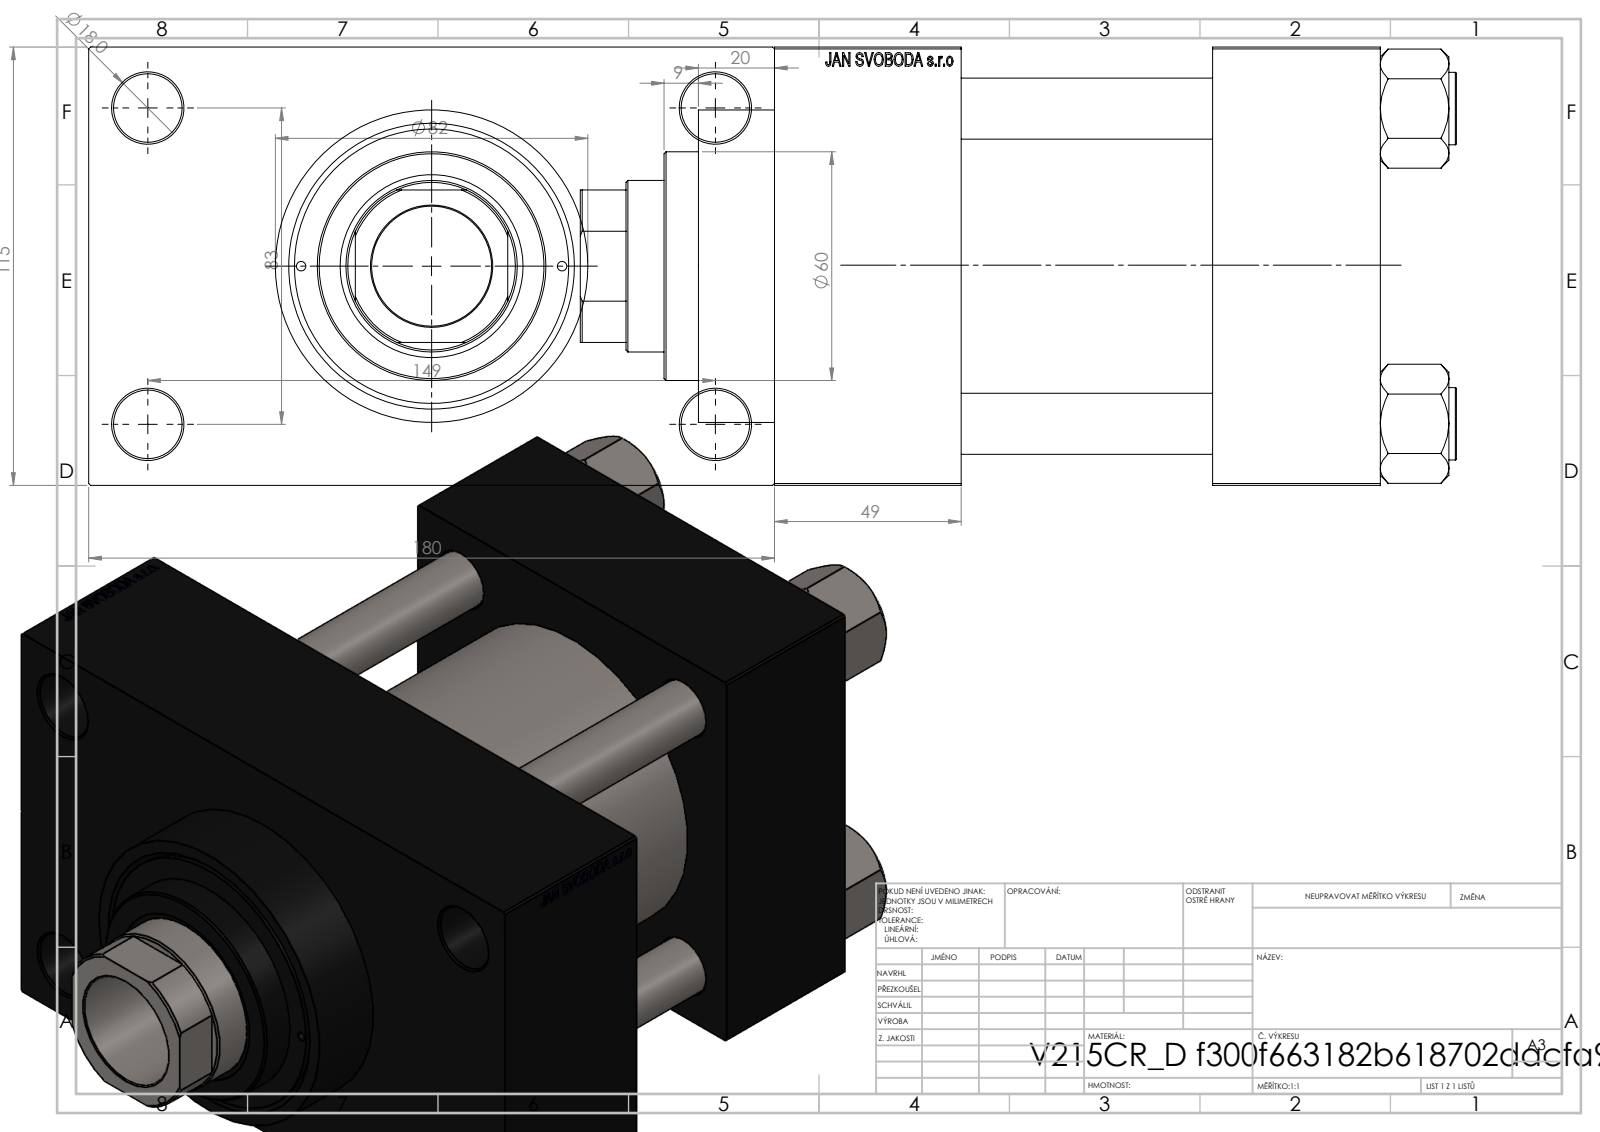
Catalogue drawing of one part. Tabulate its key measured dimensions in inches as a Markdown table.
| quantity | value |
| --- | --- |
| part name | V215CR_D_Body; V215CR_VCP_D; V215CR_D_TYCINKA; NUT_M5_D (+1 more) |
| STEP written by | SolidWorks 2019 (CONFIG_CONTROL_DESIGN) |
| units | inches |
| bodies | 11 solids, 1159 faces (547 planar, 92 cylindrical, 520 other) |
| overall size | 9.055 × 7.087 × 4.528 |
| volume | 122.3 in³ |
| surface area | 468.6 in² |
| round holes (diameter × count) | 0.63 × 4, 0.709 × 4, 0.098 × 2, 0.276 × 2, 1.041 × 2, 1.378 × 2, 1.24 × 1, 1.772 × 1, 1.89 × 1, 2.402 × 1, 2.835 × 1, 3.15 × 1 |
| round bosses / shafts (diameter × count) | 0.748 × 4, 3.386 × 1, 3.228 × 1, 2.362 × 1 |
| partial cylindrical surfaces (radius × count) | 0.866 × 1 |
| main face-to-face distances | 4.528, 4.331, 2.598, 1.929, 1.732, 6.26, 1.28, 5.807, 0.787, 2.717 |
| hole center spacings | 1.305, 1.652, 2.276, 2.302, 3.256, 3.357, 3.393, 3.513 |
